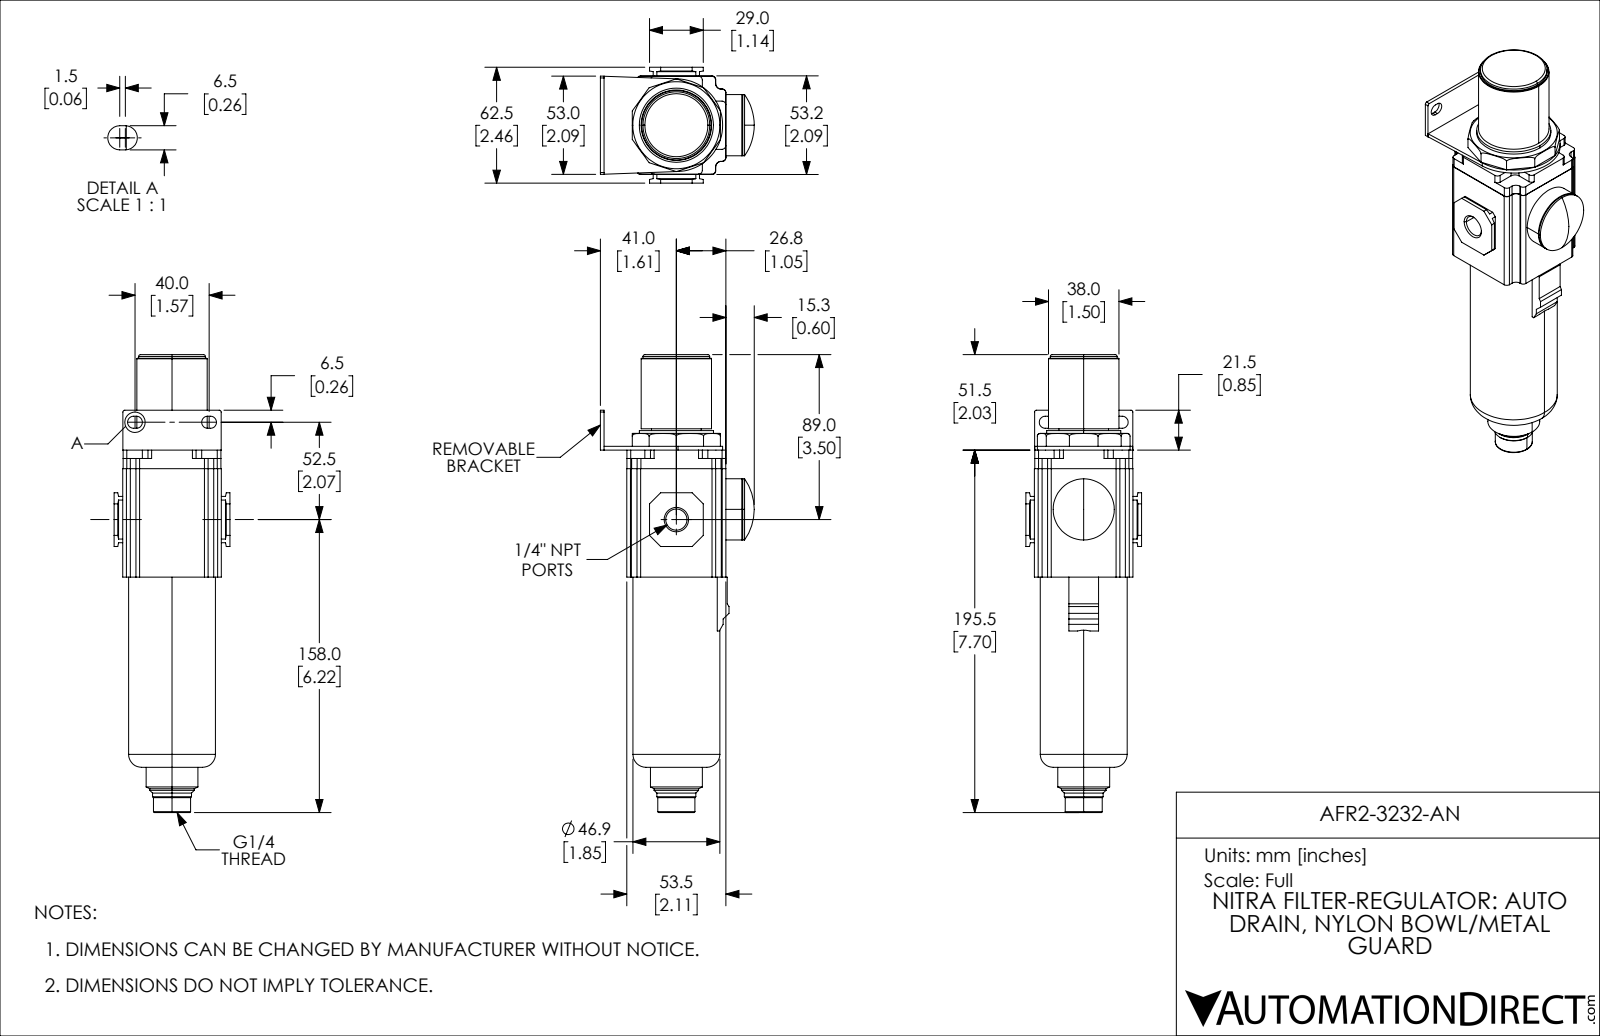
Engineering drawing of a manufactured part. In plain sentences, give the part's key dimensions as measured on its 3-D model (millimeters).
The part is named "AFR2-3232-AN". Its 3-D file was written by "SolidWorks 2019 (CONFIG_CONTROL_DESIGN)". It is 1 solid with 221 faces: 124 planar, 71 cylindrical and 26 other. Overall it measures 247 by 83.03 by 62.5 millimeters. Its volume is 452 721 cubic millimeters and its surface area 51 631 square millimeters. Round holes: 2 of diameter 11.45. Round bosses or shafts: 1 of diameter 46.9, 1 of diameter 40, 1 of diameter 38, 1 of diameter 36, 1 of diameter 33, 1 of diameter 28, 1 of diameter 26.78, 1 of diameter 24. Partial cylindrical surfaces (rounded edges, fillets, slot ends): 24 of radius 2, 12 of radius 3, 4 of radius 3.25, 2 of radius 1, 1 of radius 25. The main face-to-face distances are 2, 53.2, 53.5, 4.65, 57.85, 14.25, 12.25, 67.75, 51.5, 49.5.
